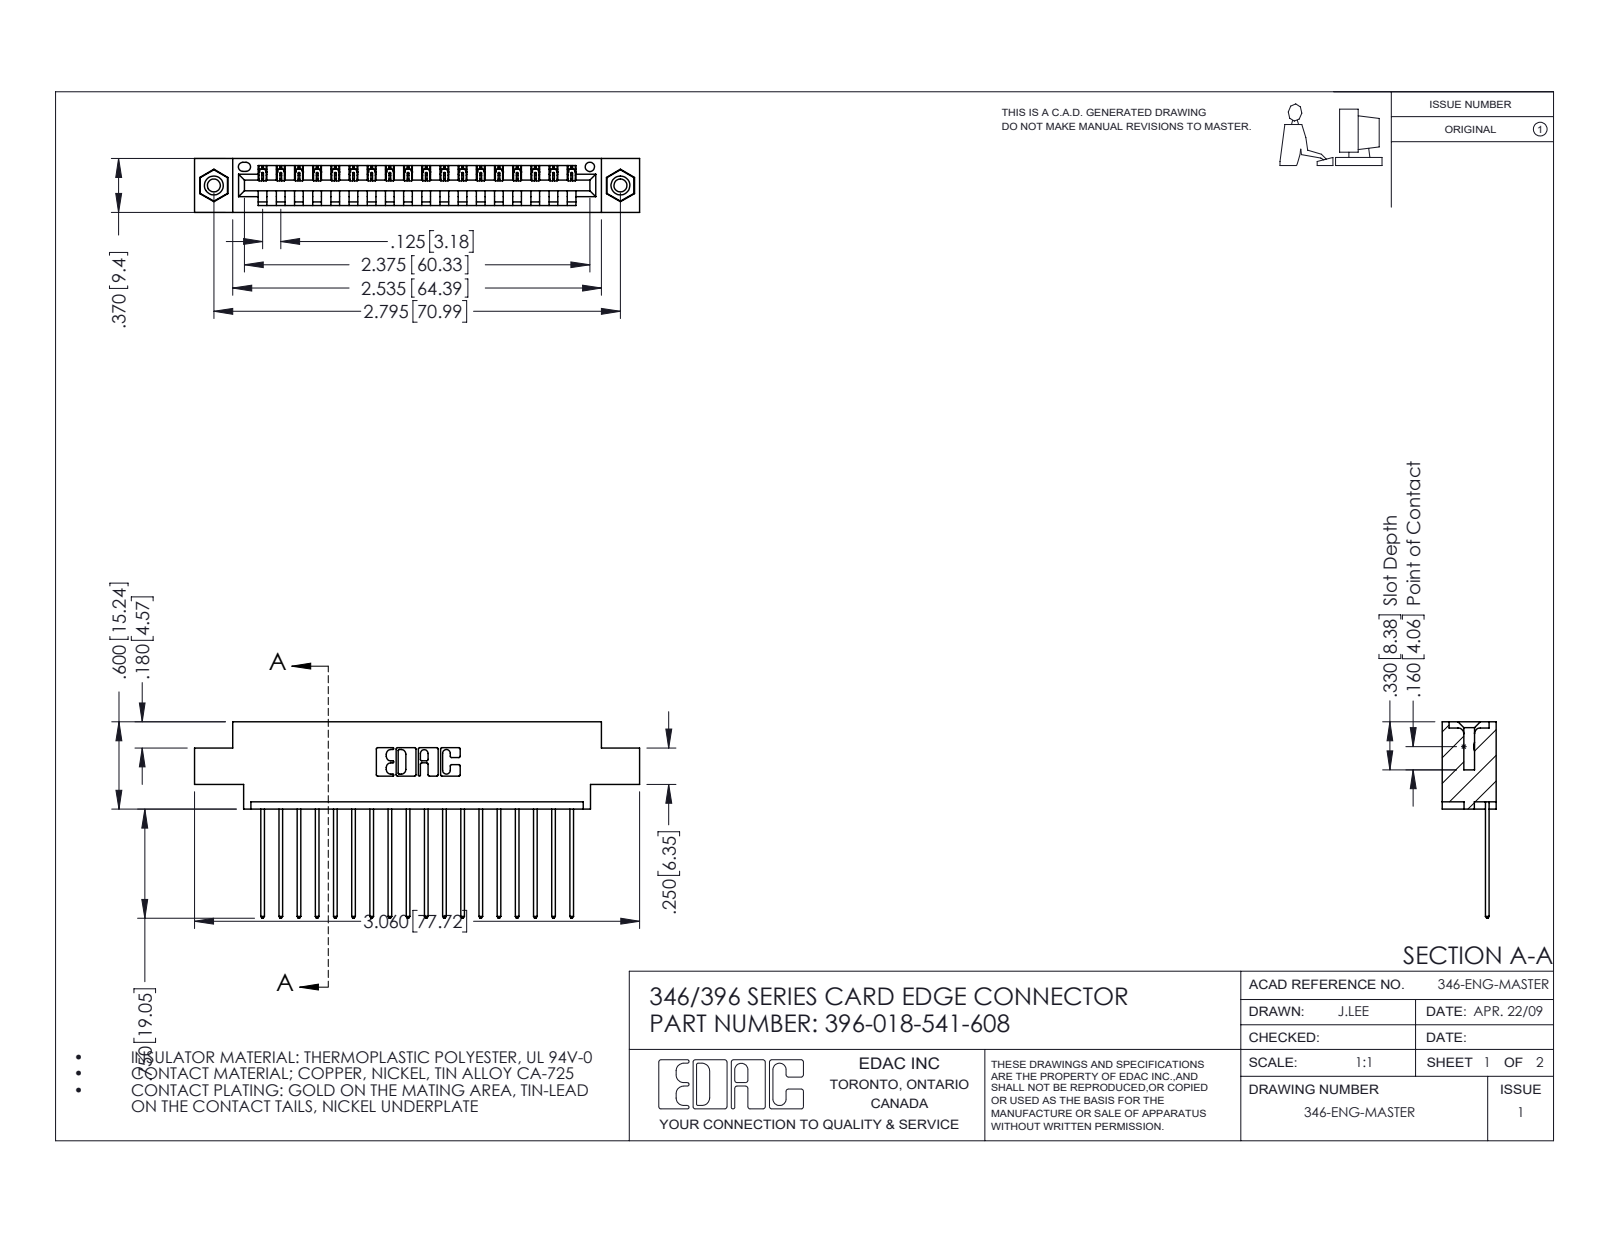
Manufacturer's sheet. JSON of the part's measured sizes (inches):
{"part_name": "345-250-001_345-250-003-102; 346 Part_0.170 Offset - 0.156 Dia-TI; 345-292-001_345-293-141; 396-018-541-608", "step_written_by": "SolidWorks 2016 (CONFIG_CONTROL_DESIGN)", "units": "inches", "bodies": {"solids": 21, "faces": 1230, "planar": 832, "cylindrical": 382, "other": 16}, "overall_size": [3.06, 1.35, 0.37], "volume_in3": 0.438, "surface_area_in2": 14.33, "round_holes": [[0.089, 2], [0.125, 2], [0.156, 2], [0.064, 1]], "round_bosses_or_shafts": [[0.155, 2]], "partial_cylinders_radius": [[0.006, 36], [0.01, 36], [0.01, 22], [0.007, 6], [0.031, 6], [0.026, 3], [0.031, 2], [0.04, 2]], "face_to_face_distances": [0.048, 0.322, 0.37, 0.25, 0.072, 0.298, 0.025, 0.222, 0.148, 0.1], "hole_center_spacings": [0.246, 2.588, 2.795]}
